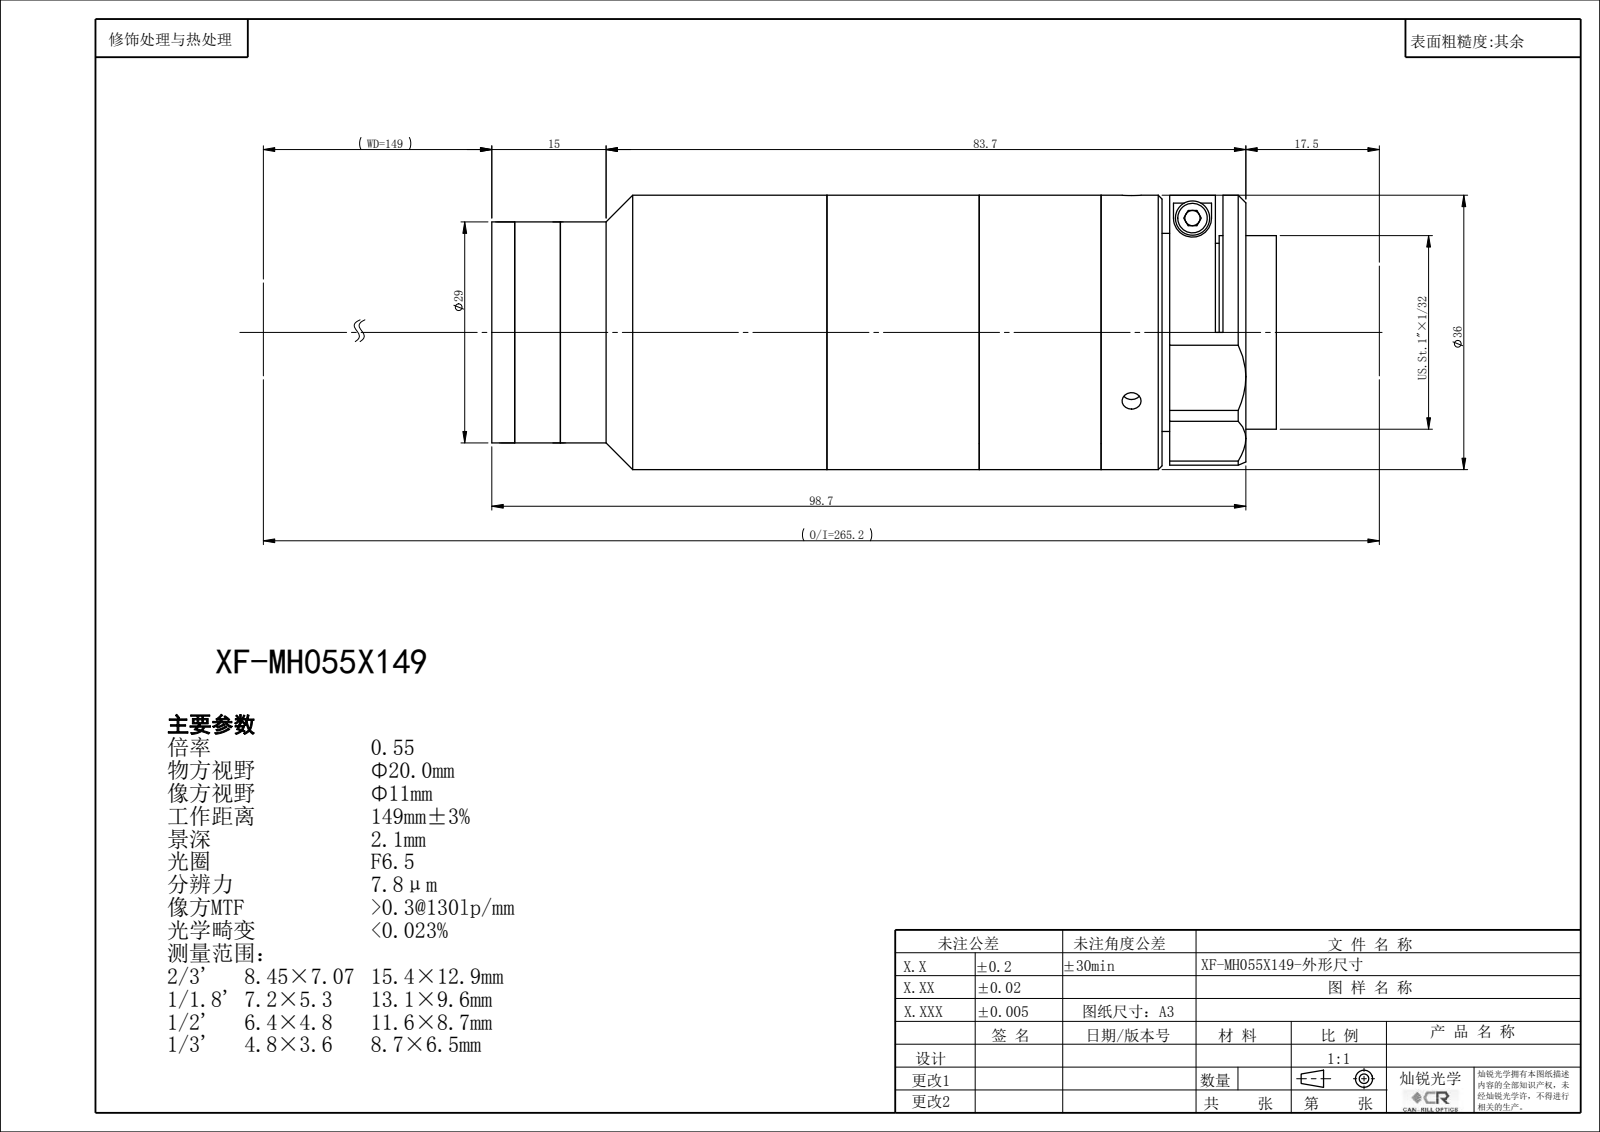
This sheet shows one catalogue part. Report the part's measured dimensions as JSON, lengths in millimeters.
{"part_name": "XF-MH055X149", "step_written_by": "SolidWorks 2022 (CONFIG_CONTROL_DESIGN)", "units": "millimeters", "bodies": {"solids": 0, "faces": 121, "planar": 59, "cylindrical": 40, "other": 22}, "overall_size": [102.67, 36, 36], "round_holes": [[2.5, 3], [18, 1], [22.4, 1], [24, 1], [24.9, 1], [26.4, 1]], "round_bosses_or_shafts": [[36, 1], [34, 1], [29, 1], [25.4, 1]], "face_to_face_distances": [18.67, 1.5, 17.17, 16, 33.17, 34.67, 20, 36, 53.17, 54.67]}
